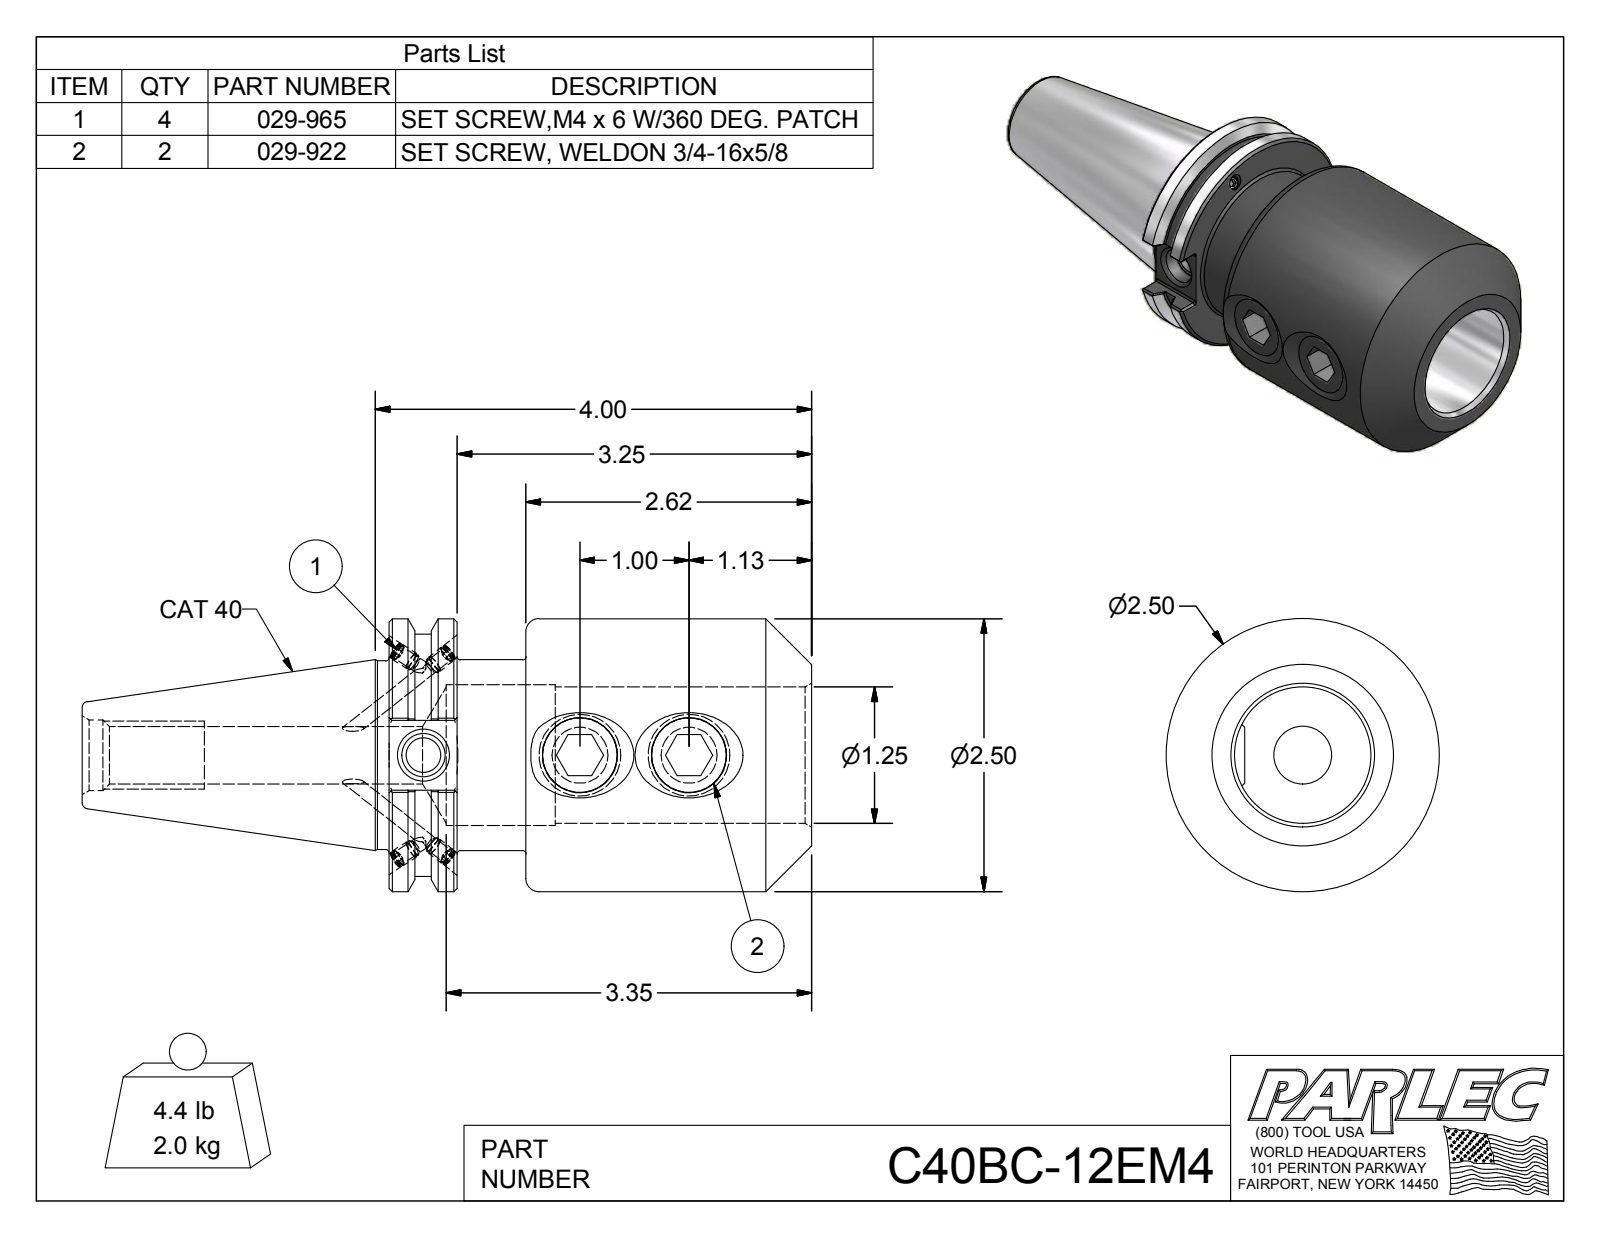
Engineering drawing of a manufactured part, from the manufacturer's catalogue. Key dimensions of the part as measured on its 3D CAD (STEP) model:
Part name (STEP PRODUCT): C40BC-12EM4; C40BC-12EM4-1; 029-922; 029-965
STEP written by: Autodesk Inventor 2012 (AUTOMOTIVE_DESIGN)
Units: inches
Bodies: 7 solids, 199 faces (96 planar, 51 cylindrical, 52 other)
Overall size (bounding box): 6.687 × 2.5 × 2.5
Volume: 15.51 in³ · Surface area: 78.76 in²
Round holes (diameter × count): ⌀0.13 ×4, ⌀0.161 ×4, ⌀0.682 ×2, ⌀0.315 ×1, ⌀0.399 ×1, ⌀0.527 ×1, ⌀0.648 ×1, ⌀1.25 ×1, ⌀1.29 ×1
Round bosses / shafts (diameter × count): ⌀0.165 ×4, ⌀0.157 ×4, ⌀0.75 ×2, ⌀2.5 ×1, ⌀2.219 ×1, ⌀1.75 ×1, ⌀1.73 ×1
Partial cylindrical surfaces — rounded edges, fillets, slot ends (radius × count): R0.02 ×12
Main face-to-face distances: 0.625, 1.255, 0.63, 3.875, 3.25, 2.62, 0.625, 0.375, 1.42, 2.046
Hole centre spacings: 1, 1.435, 2.435
